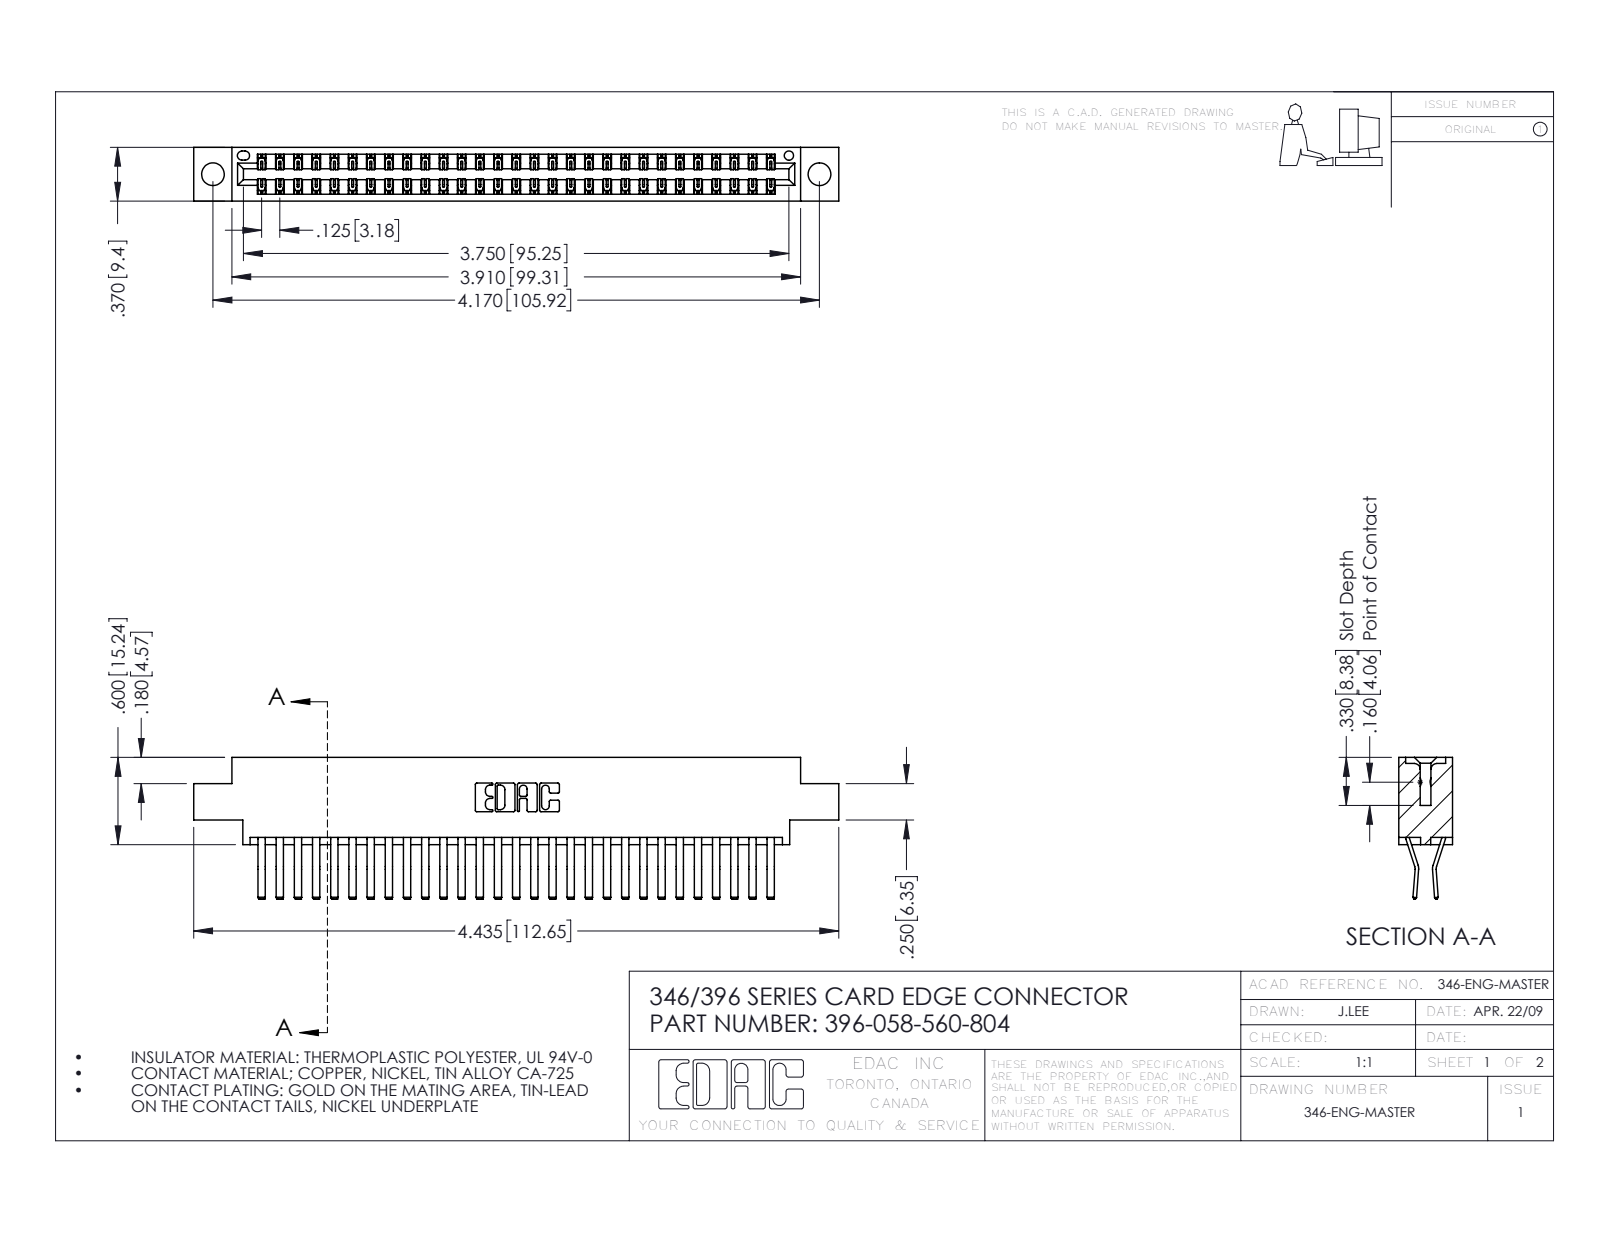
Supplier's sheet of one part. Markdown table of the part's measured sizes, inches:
| quantity | value |
| --- | --- |
| part name | 345-292-001_560 Tail; 346 Part_0.170 Offset - 0.156 Dia-TH; 396-058-560-804 |
| STEP written by | SolidWorks 2016 (CONFIG_CONTROL_DESIGN) |
| units | inches |
| bodies | 59 solids, 3258 faces (2110 planar, 1148 cylindrical, 0 other) |
| overall size | 4.435 × 0.975 × 0.37 |
| volume | 0.673 in³ |
| surface area | 24.73 in² |
| round holes (diameter × count) | 0.156 × 2, 0.064 × 1 |
| partial cylindrical surfaces (radius × count) | 0.006 × 87, 0.01 × 22, 0.007 × 6, 0.031 × 6, 0.026 × 3, 0.01 × 2, 0.014 × 2, 0.022 × 2 |
| main face-to-face distances | 0.048, 0.322, 0.37, 0.025, 0.25, 0.072, 0.298, 0.275, 0.148, 0.222 |
| hole center spacings | 0.246, 3.962, 4.17 |
